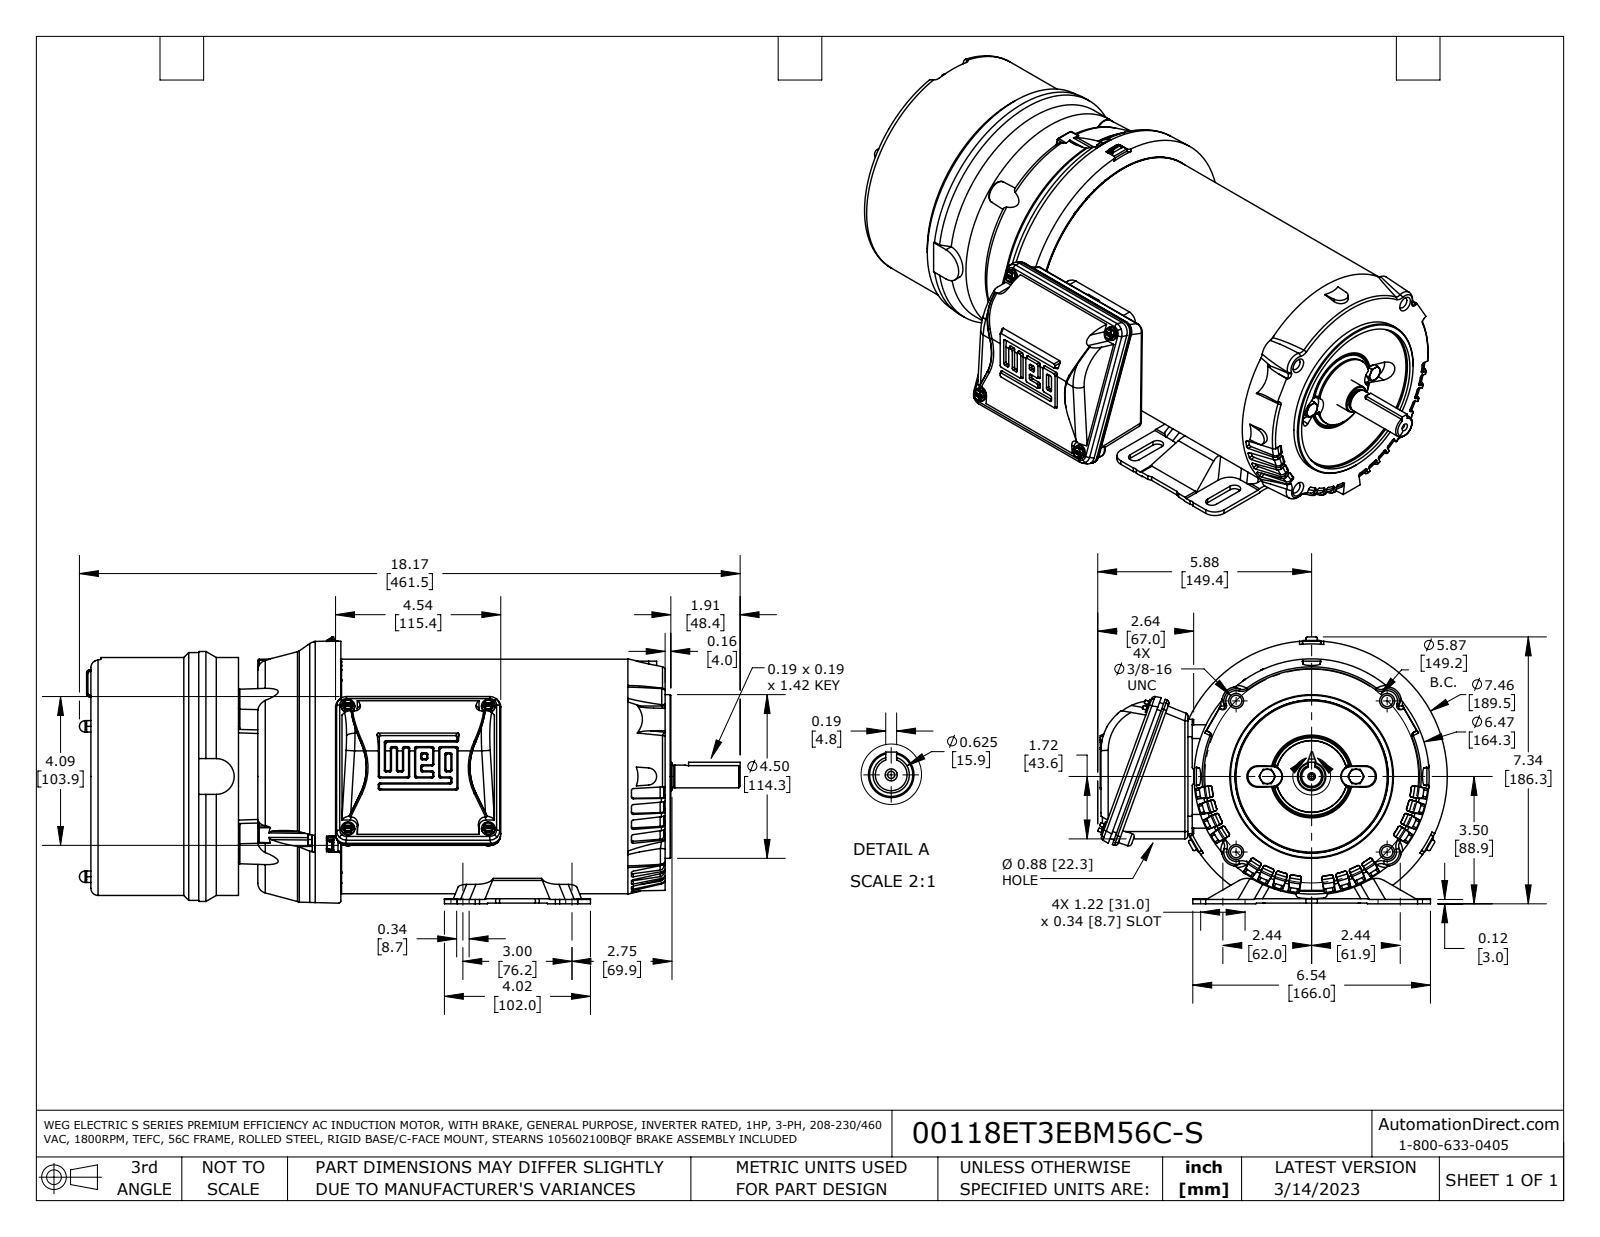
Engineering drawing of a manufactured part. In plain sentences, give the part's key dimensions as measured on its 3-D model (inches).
The part is named "56C_3PH_TEFC_BM_17976 coord fxt". Its 3-D file was written by "SolidWorks 2021 (AUTOMOTIVE_DESIGN)". It is 16 solids with 1525 faces: 598 planar, 406 cylindrical and 521 other. Overall it measures 18.169 by 9.612 by 7.337 inches. Its volume is 554.4 cubic inches and its surface area 833 square inches. Round holes: 4 of diameter 0.313, 1 of diameter 0.124. Round bosses or shafts: 4 of diameter 0.374, 3 of diameter 0.315, 3 of diameter 0.256, 2 of diameter 0.35, 1 of diameter 6.87, 1 of diameter 6.811, 1 of diameter 6.54, 1 of diameter 6.457. Partial cylindrical surfaces (rounded edges, fillets, slot ends): 51 of radius 0.039, 40 of radius 0.047, 32 of radius 0.051, 16 of radius 0.02, 16 of radius 0.079, 12 of radius 0.087, 8 of radius 0.171, 8 of radius 0.205. The main face-to-face distances are 7.874, 10.709, 2.835, 4.059, 6.894, 14.768, 4.591, 0.531, 2.303, 10.177. The hole center spacings are 2.937, 4.154, 5.874.
